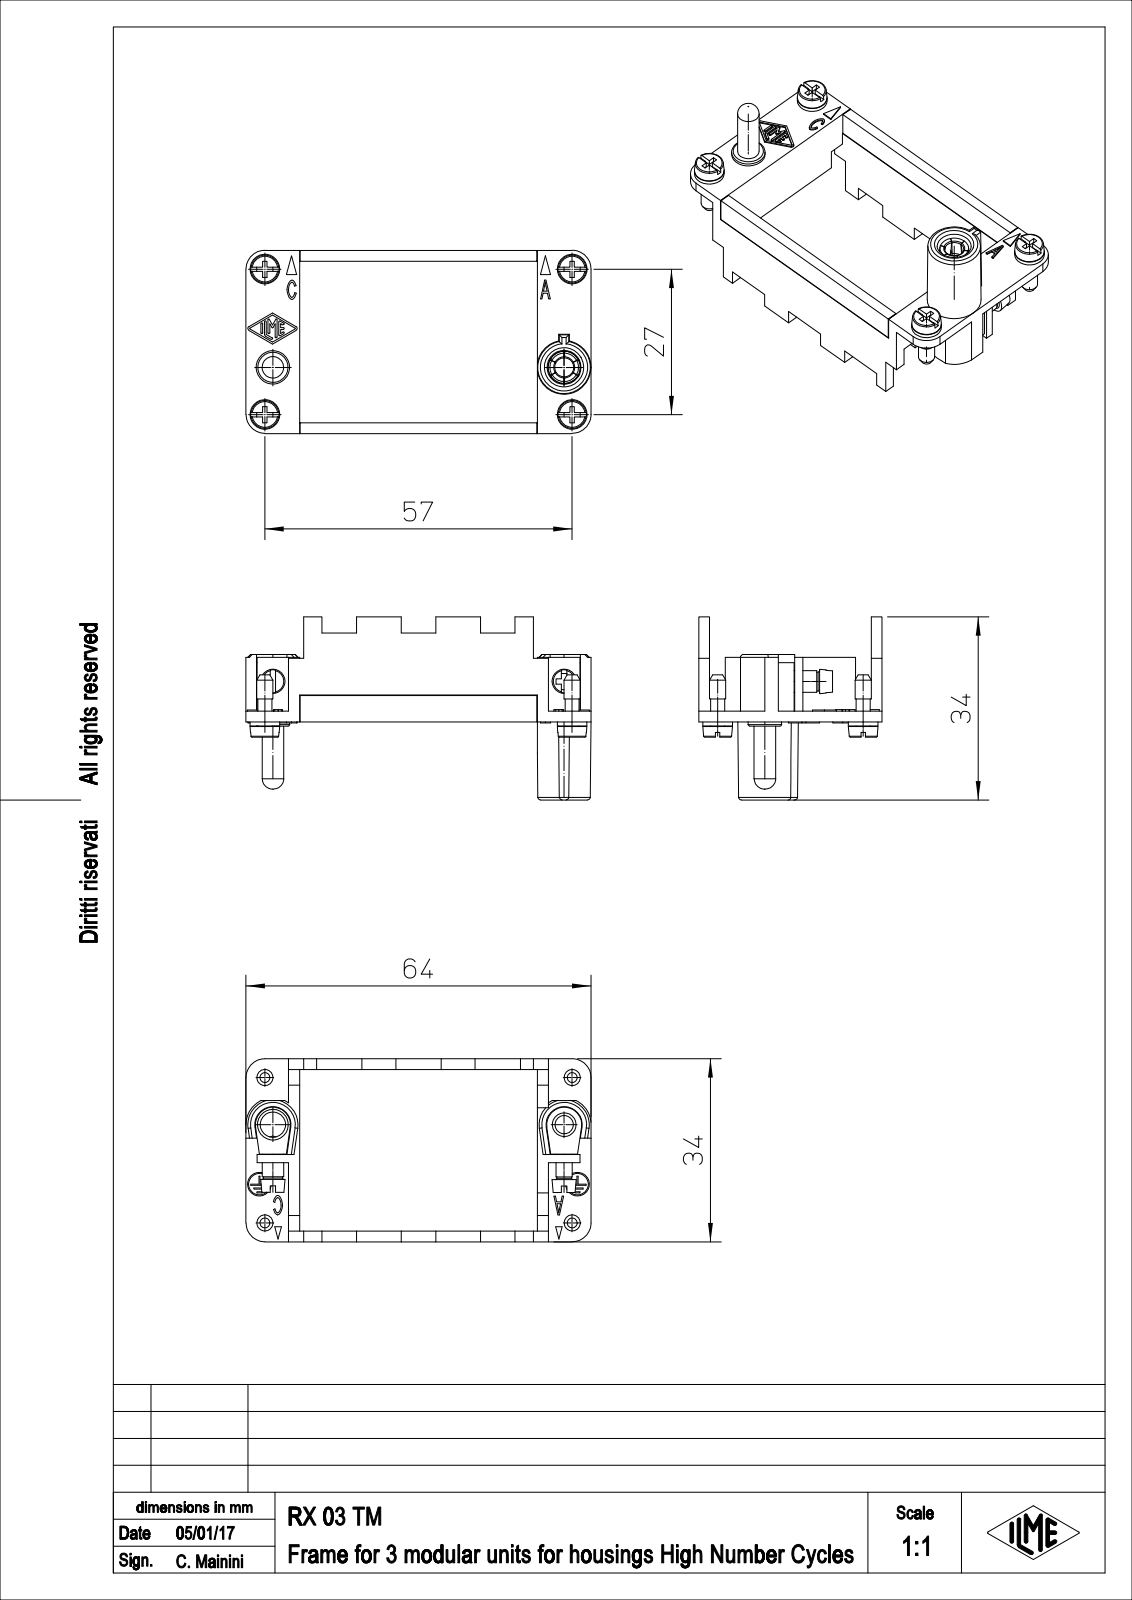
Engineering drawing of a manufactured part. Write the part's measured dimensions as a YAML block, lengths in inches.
part_name: "RX_03_TM"
step_written_by: "PTC Creo Elements/Direct Modeling 19.0E 27-Jun-2016 (C) Parametric Technology GmbH (AUTOMOTIVE_DESIGN)"
units: inches
bodies: {solids: 1, faces: 613, planar: 401, cylindrical: 103, other: 109}
overall_size: [2.52, 1.339, 1.339]
volume: 0.515
surface_area: 16.06
round_holes:
  - {diameter: 0.157, count: 2}
  - {diameter: 0.098, count: 1}
  - {diameter: 0.13, count: 1}
  - {diameter: 0.134, count: 1}
  - {diameter: 0.165, count: 1}
  - {diameter: 0.185, count: 1}
  - {diameter: 0.248, count: 1}
round_bosses_or_shafts:
  - {diameter: 0.118, count: 5}
  - {diameter: 0.217, count: 4}
  - {diameter: 0.102, count: 4}
  - {diameter: 0.173, count: 2}
  - {diameter: 0.157, count: 2}
  - {diameter: 0.244, count: 1}
  - {diameter: 0.236, count: 1}
  - {diameter: 0.138, count: 1}
partial_cylinders:
  - {radius: 0.007, count: 11}
  - {radius: 0.138, count: 4}
  - {radius: 0.02, count: 3}
  - {radius: 0.005, count: 2}
  - {radius: 0.016, count: 2}
  - {radius: 0.128, count: 2}
  - {radius: 0.197, count: 2}
  - {radius: 0.013, count: 1}
face_to_face_distances: [0.079, 1.26, 1.339, 1.181, 0.081, 1.817, 1.736, 0.392, 1.898, 0.311]
hole_center_spacings: [0.446, 2.127, 0.446, 2.126, 2.267, 2.267, 2.268, 2.323]
